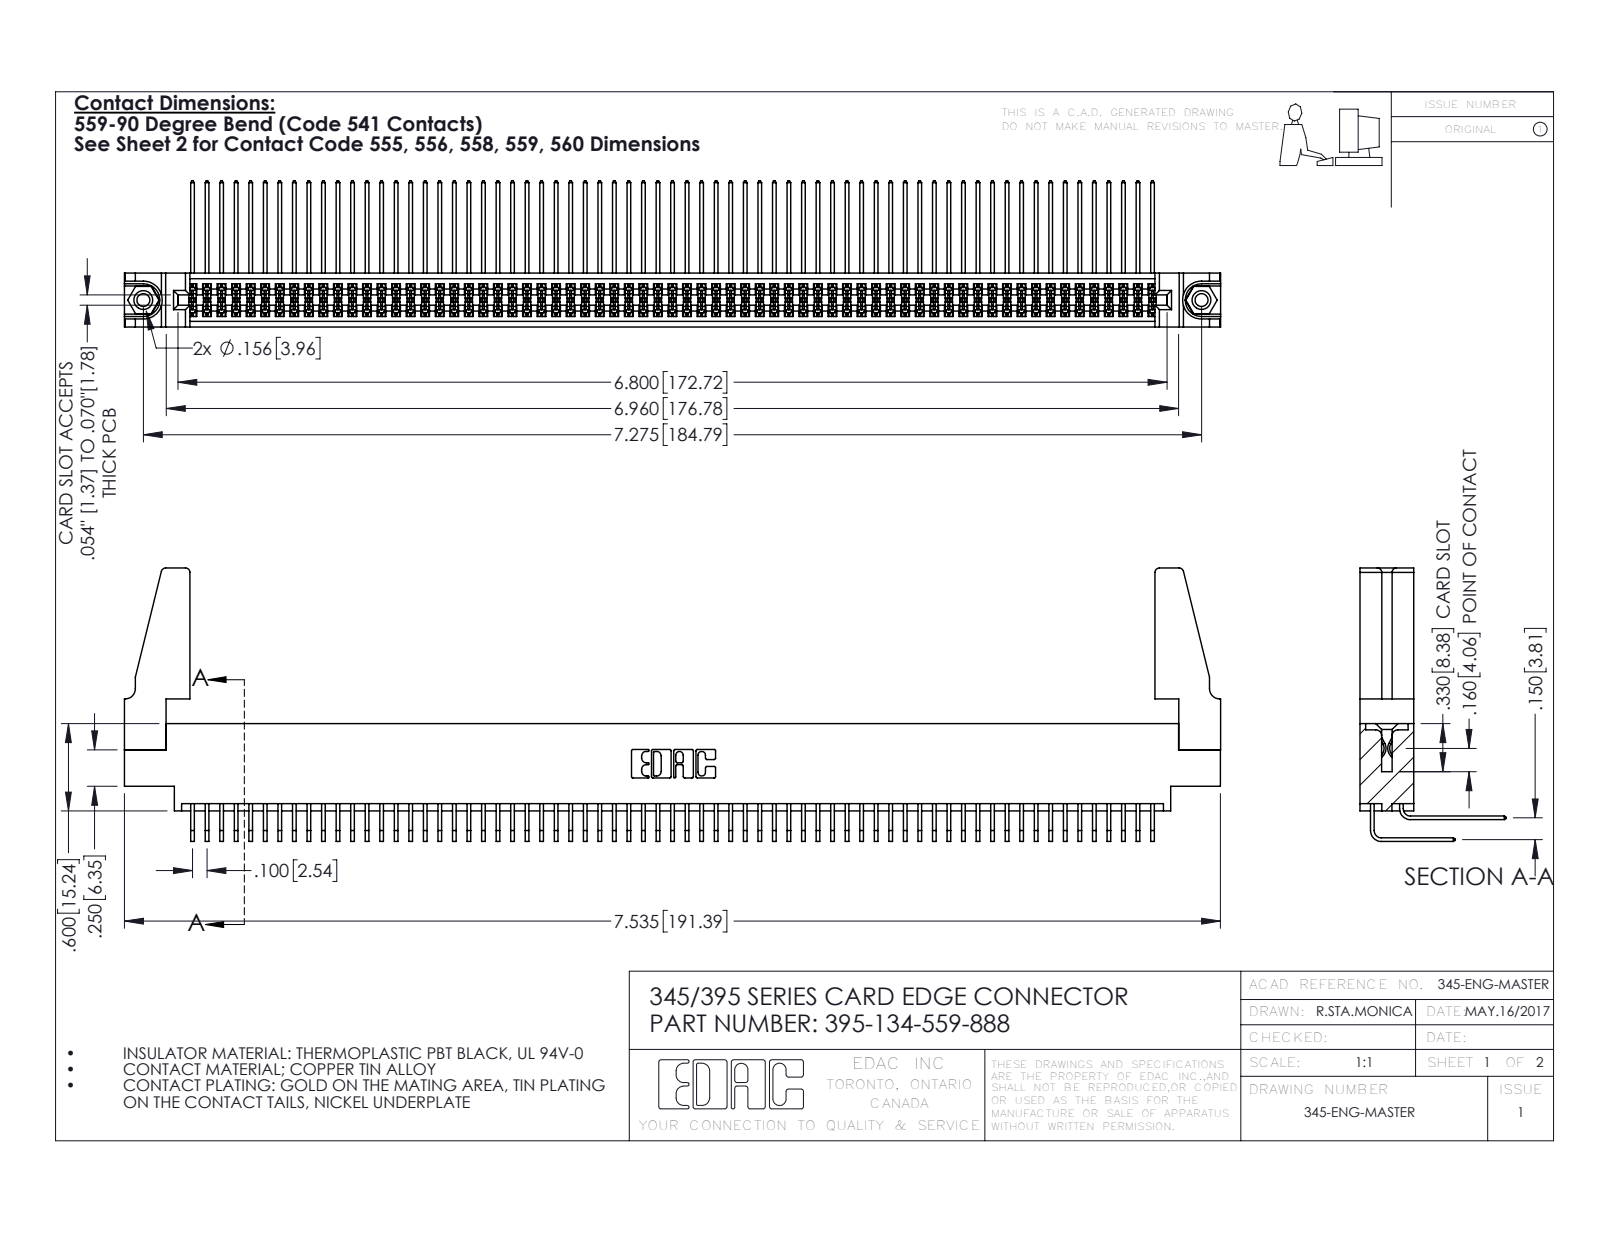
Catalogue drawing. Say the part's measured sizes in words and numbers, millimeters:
The part is named "345-292-001_558 559 Tail - 1; 345 Part_0.170 Offset - 0.156 Dia-TH; 345-250-001_345-250-001-102; 395-134-559-888 (+2 more)". Its 3-D file was written by "SolidWorks 2016 (CONFIG_CONTROL_DESIGN)". It is 139 solids with 7222 faces: 4846 planar, 2360 cylindrical and 16 other. Overall it measures 191.4 by 47.7 by 25.5 millimeters. Its volume is 22 750 cubic millimeters and its surface area 36 190 square millimeters. Round holes: 2 of diameter 2.3, 2 of diameter 3.2, 2 of diameter 4, 1 of diameter 1.6. Round bosses or shafts: 2 of diameter 3.9. Partial cylindrical surfaces (rounded edges, fillets, slot ends): 201 of radius 0.2, 22 of radius 0.3, 8 of radius 0.8, 6 of radius 0.2, 6 of radius 0.8, 3 of radius 0.7, 2 of radius 0.4, 2 of radius 0.5. The main face-to-face distances are 1.8, 7.6, 9.4, 2.5, 6.9, 0.6, 5.1, 5.7, 4.4, 3.8. The hole center spacings are 6.9, 178.8, 184.8.
